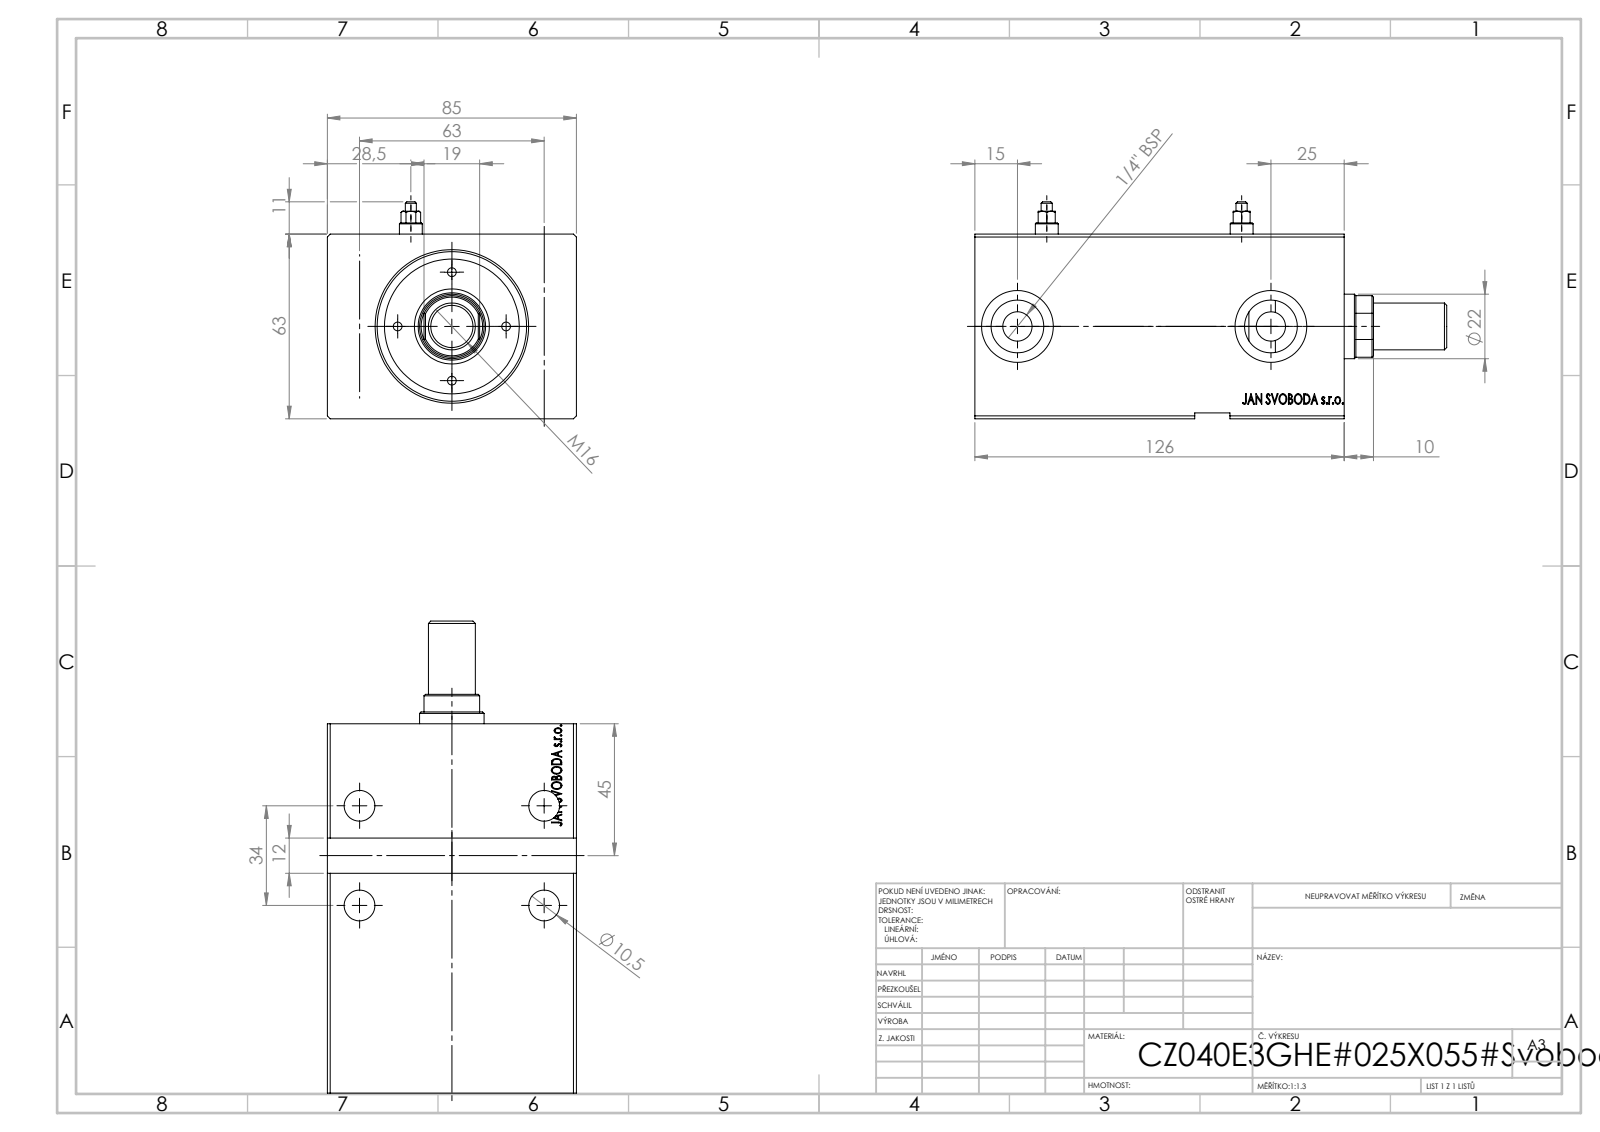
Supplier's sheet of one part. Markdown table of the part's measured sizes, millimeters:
| quantity | value |
| --- | --- |
| STEP written by | SolidWorks 2019 (CONFIG_CONTROL_DESIGN) |
| units | millimeters |
| bodies | 1 solid, 781 faces (384 planar, 31 cylindrical, 366 other) |
| overall size | 126 × 85 × 63 |
| volume | 496 337 mm³ |
| surface area | 71 369 mm² |
| round holes (diameter × count) | 10.5 × 4, 8 × 2, 10 × 2, 18 × 2, 24.5 × 2, 36 × 1, 40 × 1, 51 × 1 |
| main face-to-face distances | 63, 85, 126, 110.7, 15.3, 2, 61, 125.8, 15.1, 10 |
| hole center spacings | 34, 63, 71.59, 18.85, 32.18, 43.2, 46.04, 52.91 |
